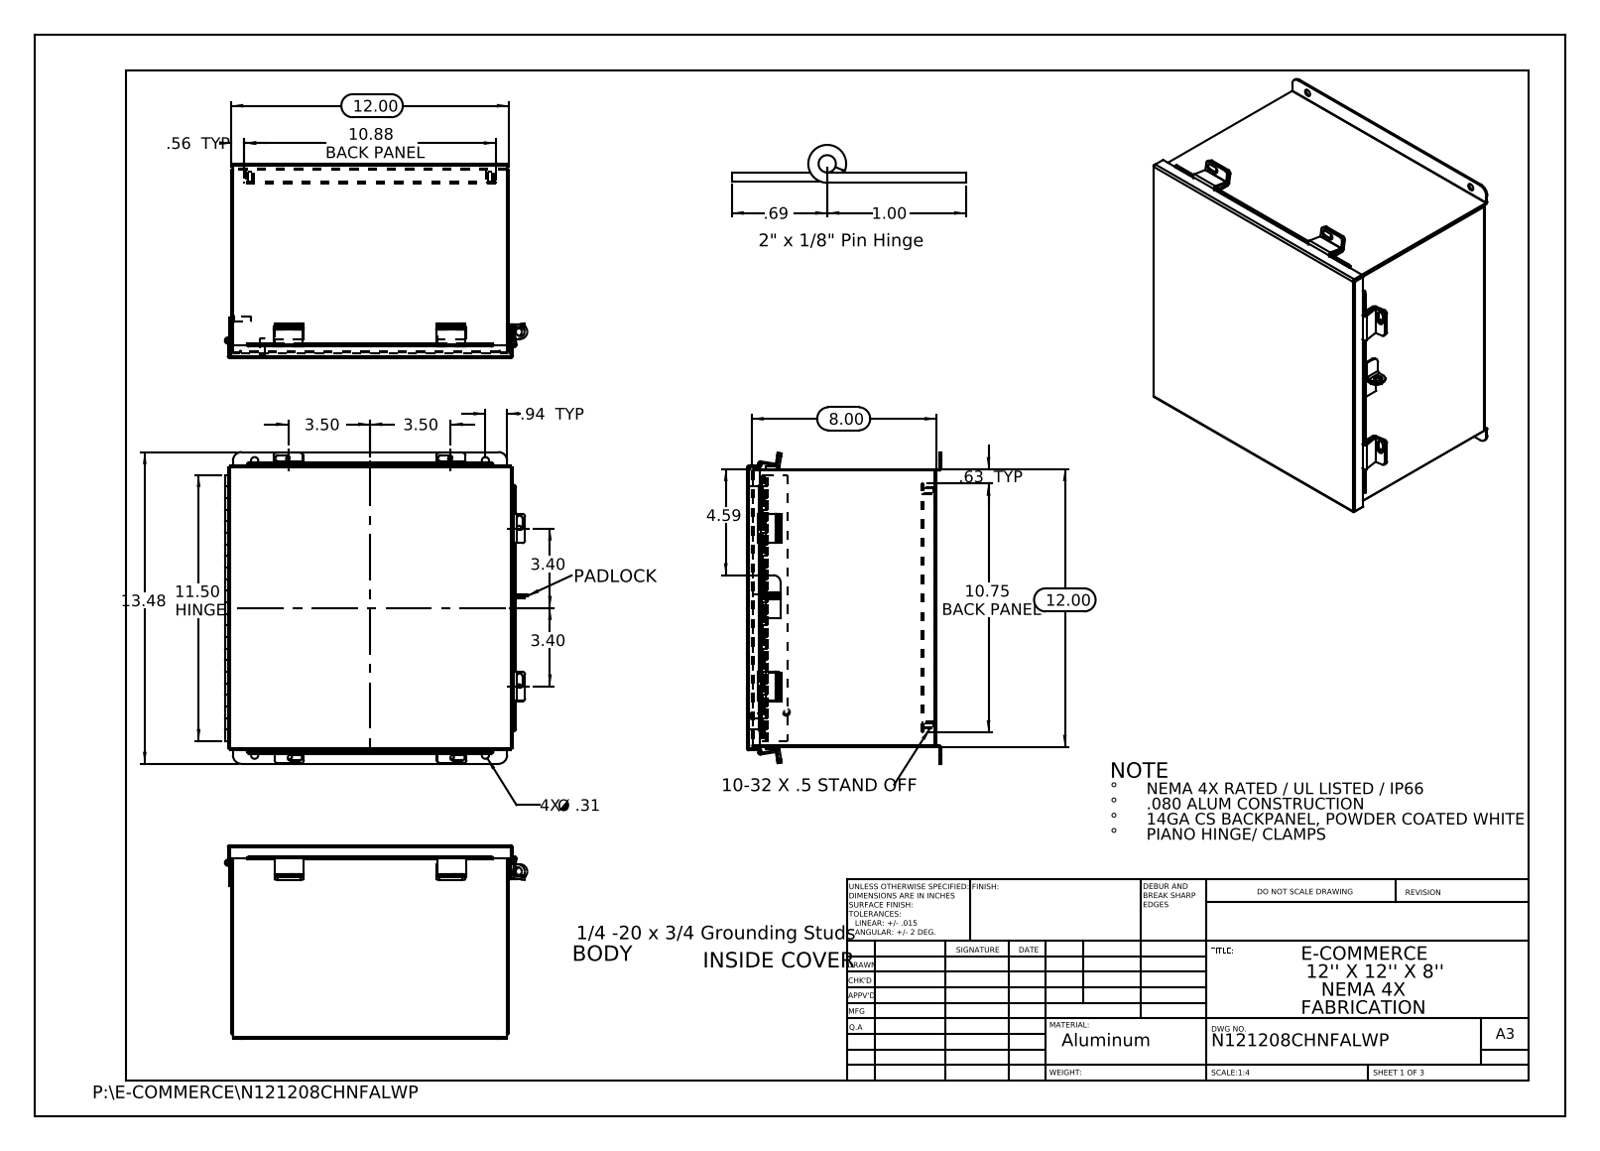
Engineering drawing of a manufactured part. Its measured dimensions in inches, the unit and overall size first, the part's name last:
Units: inches
Overall size (bounding box): 13.476 × 13.072 × 8.39
Round holes (diameter × count): ⌀0.25 ×10, ⌀0.187 ×4, ⌀0.312 ×4, ⌀0.125 ×1, ⌀0.125 ×1, ⌀0.373 ×1, ⌀0.375 ×1
Round bosses / shafts (diameter × count): ⌀0.313 ×4, ⌀0.315 ×2, ⌀0.236 ×2, ⌀0.273 ×1, ⌀0.25 ×1
Partial cylindrical surfaces — rounded edges, fillets, slot ends (radius × count): R0.125 ×21, R0.013 ×13, R0.009 ×12, R0.088 ×12, R0.133 ×12, R0.083 ×6, R0.1 ×6, R0.375 ×4
Main face-to-face distances: 0.075, 11.925, 8.128, 11.85, 12, 8.053, 8.203, 0.074, 0.575, 0.5
Hole centre spacings: 1.315, 10.258, 11.428, 15.3, 7, 9.976, 10.126, 10.375
Volume: 66.97 in³ · Surface area: 1 824 in²
Bodies: 27 solids, 794 faces (499 planar, 275 cylindrical, 20 other)
Part name (STEP PRODUCT): N121208CHNFALWP HW-CD-S-25020-034; N121208CHNFALWP JIC Top; N121208CHNFALWP JIC Clamp Bracket; HW-CLH-JH-20104 (+8 more)
STEP written by: SolidWorks 2013 (CONFIG_CONTROL_DESIGN)
